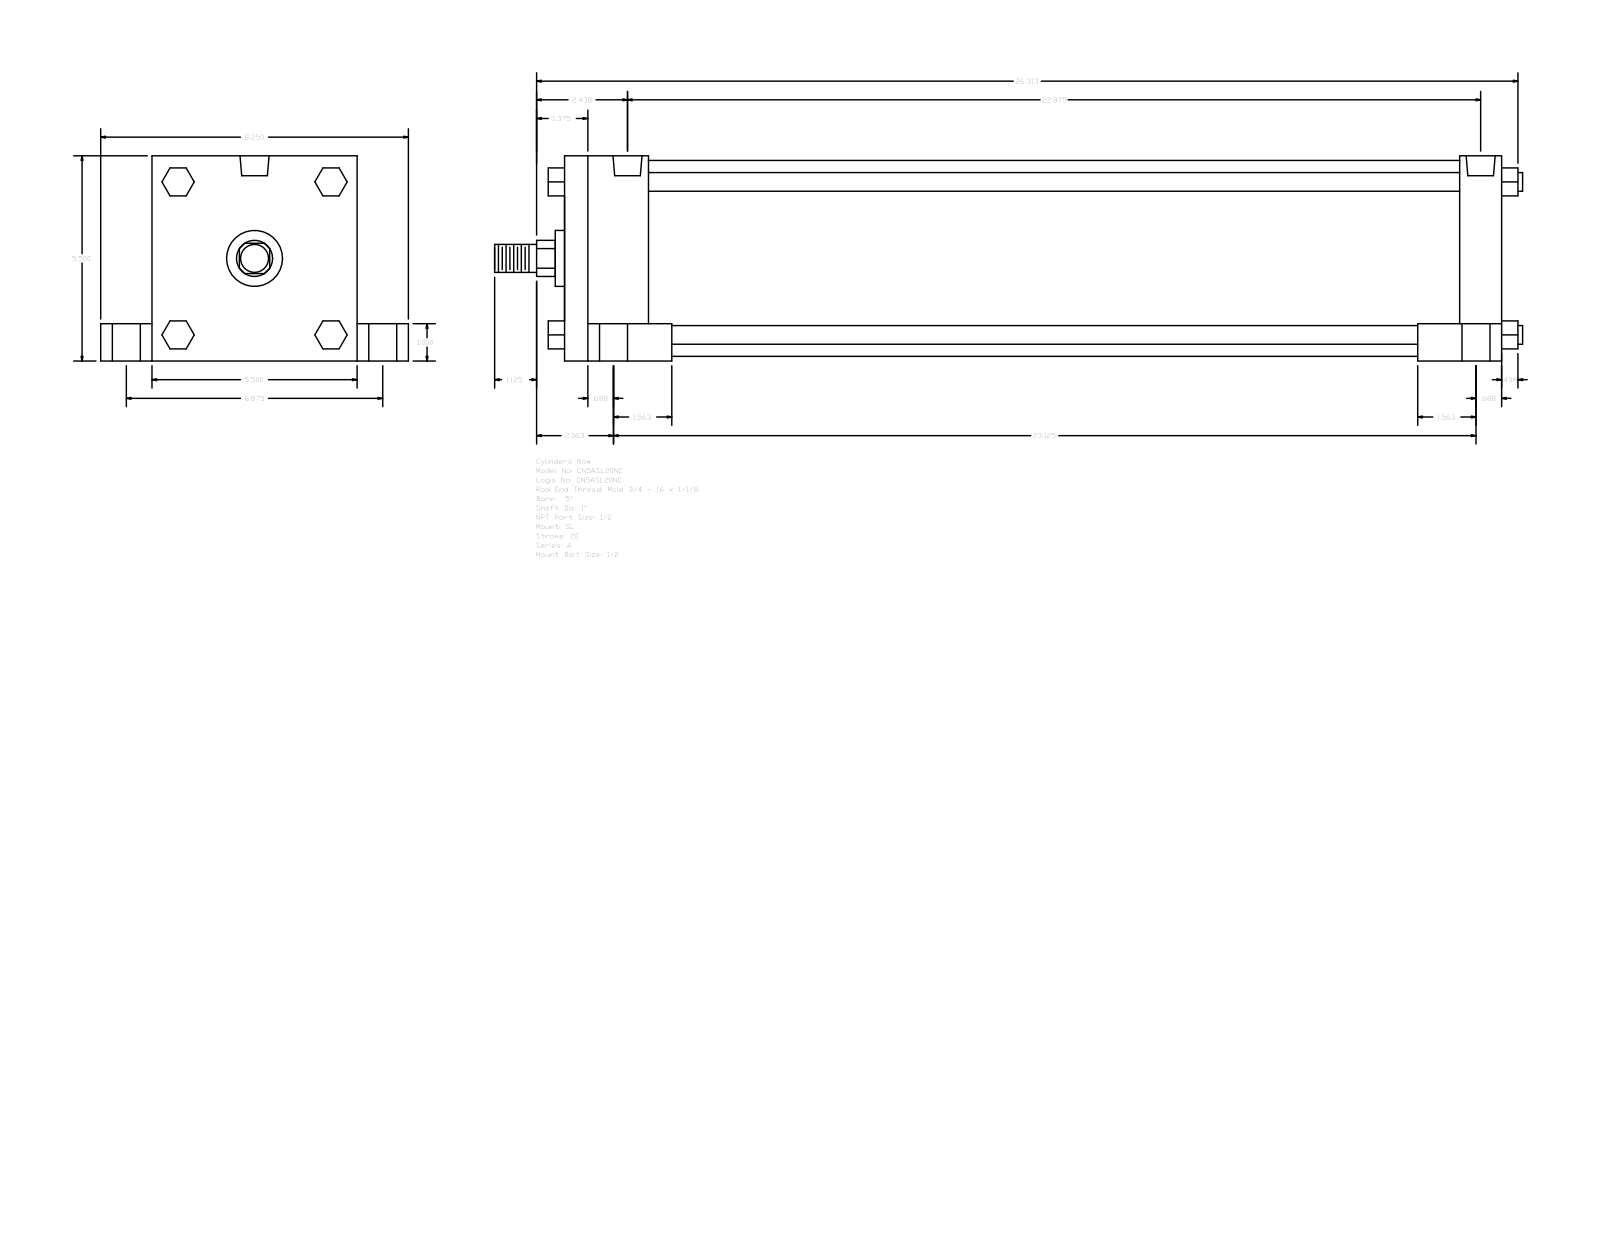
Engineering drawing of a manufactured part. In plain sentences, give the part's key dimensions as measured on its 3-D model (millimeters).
The part is named "A_SL__0500_1". Its 3-D file was written by "GSSL Pune (CONFIG_CONTROL_DESIGN)". It is 0 solids with 150 faces: 114 planar, 36 cylindrical and 0 other. Overall it measures 700.09 by 209.55 by 139.7 millimeters. Round holes: 4 of diameter 8.73, 4 of diameter 19.05, 4 of diameter 25.4, 2 of diameter 19.77. Round bosses or shafts: 4 of diameter 12.7, 1 of diameter 133.35, 1 of diameter 38.1, 1 of diameter 25.4, 1 of diameter 19.05. Partial cylindrical surfaces (rounded edges, fillets, slot ends): 1 of radius 12.29. The main face-to-face distances are 139.7, 638.18, 57.15, 581.03, 25.4, 114.3, 34.93, 174.63, 609.6, 552.45. The hole center spacings are 2.39, 87.31, 87.37, 87.83, 88.12, 174.62, 576.25, 578.64.
